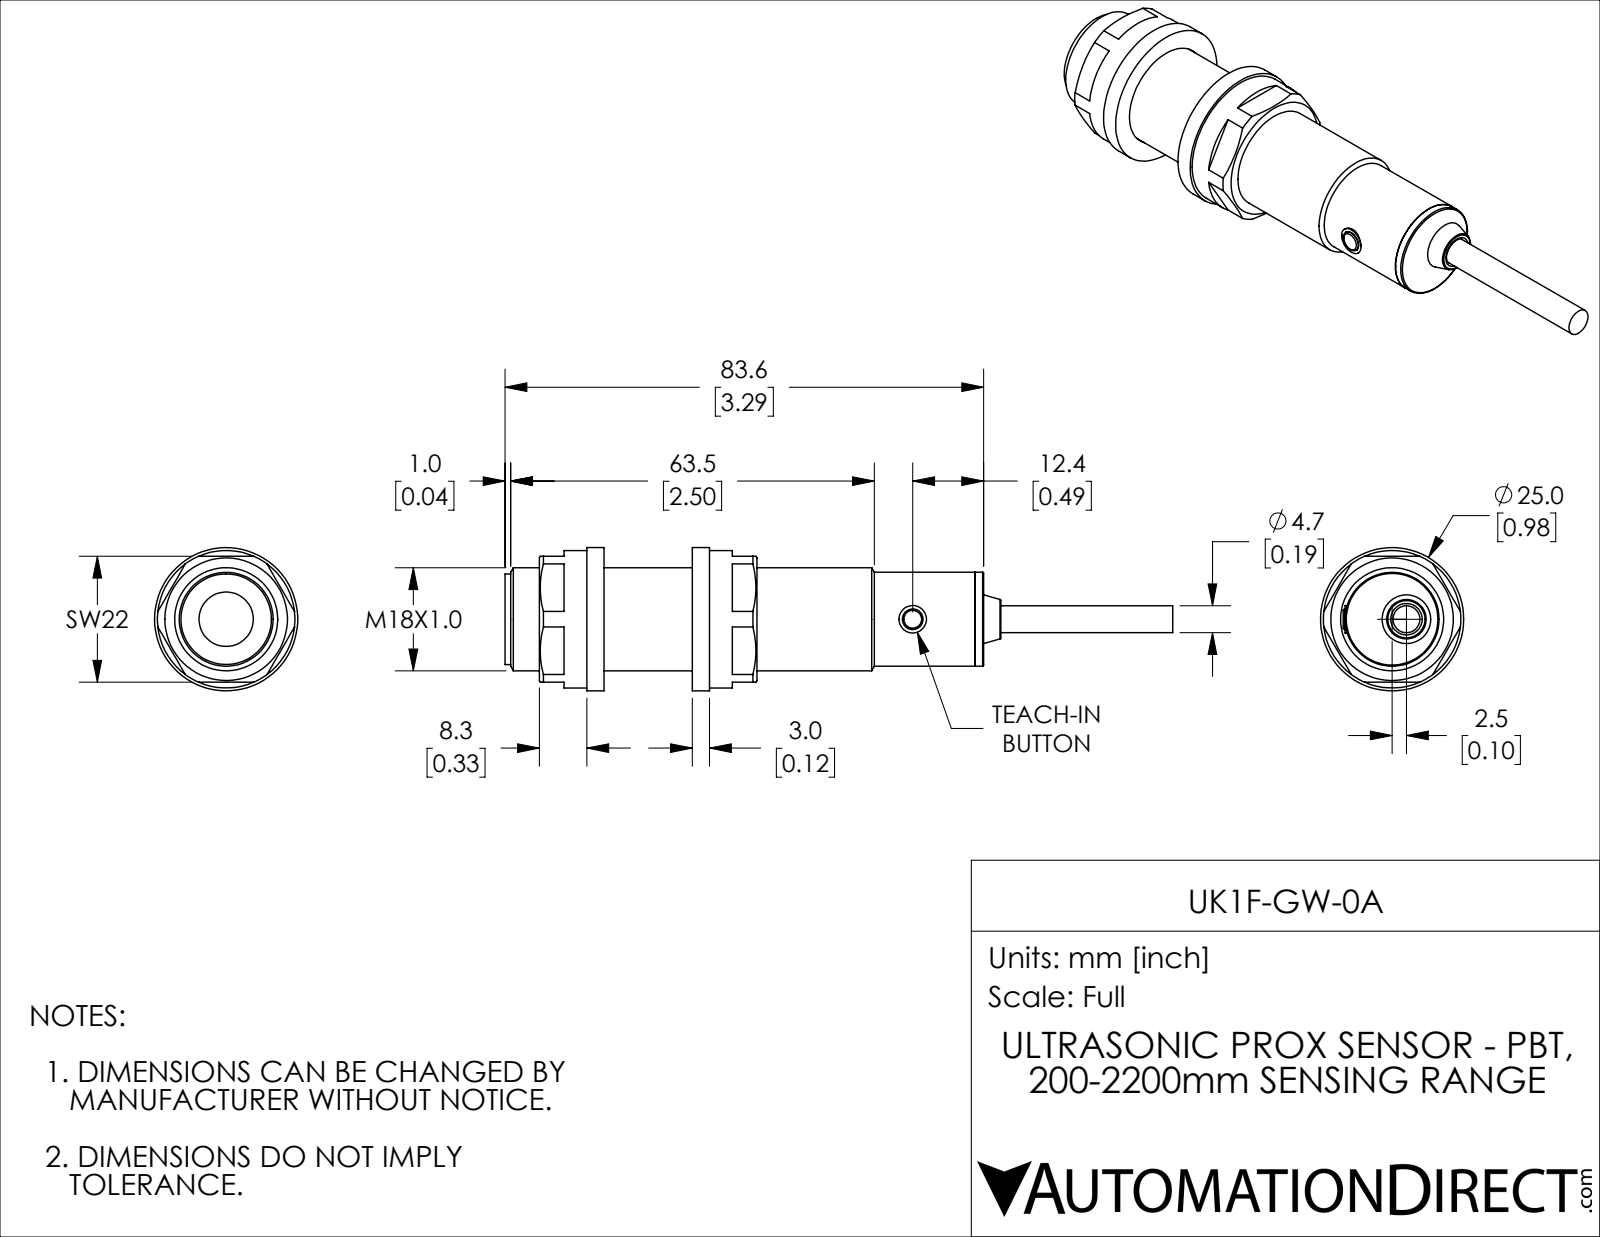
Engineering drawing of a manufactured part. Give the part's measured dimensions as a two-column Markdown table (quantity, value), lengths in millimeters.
| quantity | value |
| --- | --- |
| part name | UK1F-GW-0A |
| STEP written by | SolidWorks 2018 (AUTOMOTIVE_DESIGN) |
| units | millimeters |
| bodies | 10 solids, 107 faces (49 planar, 40 cylindrical, 18 other) |
| overall size | 116.6 × 25 × 25 |
| volume | 25 220 mm³ |
| surface area | 11 419 mm² |
| round holes (diameter × count) | 4.7 × 2, 3.6 × 1, 9.5 × 1, 18 × 1, 18.2 × 1 |
| round bosses / shafts (diameter × count) | 25 × 1, 24 × 1, 16.4 × 1, 15.8 × 1, 5.4 × 1, 4.8 × 1 |
| main face-to-face distances | 3, 18.4, 21.4, 67.8, 46.4, 13.3, 34.7, 81.1, 16.3, 64.8 |
| hole center spacings | 2.5 |
